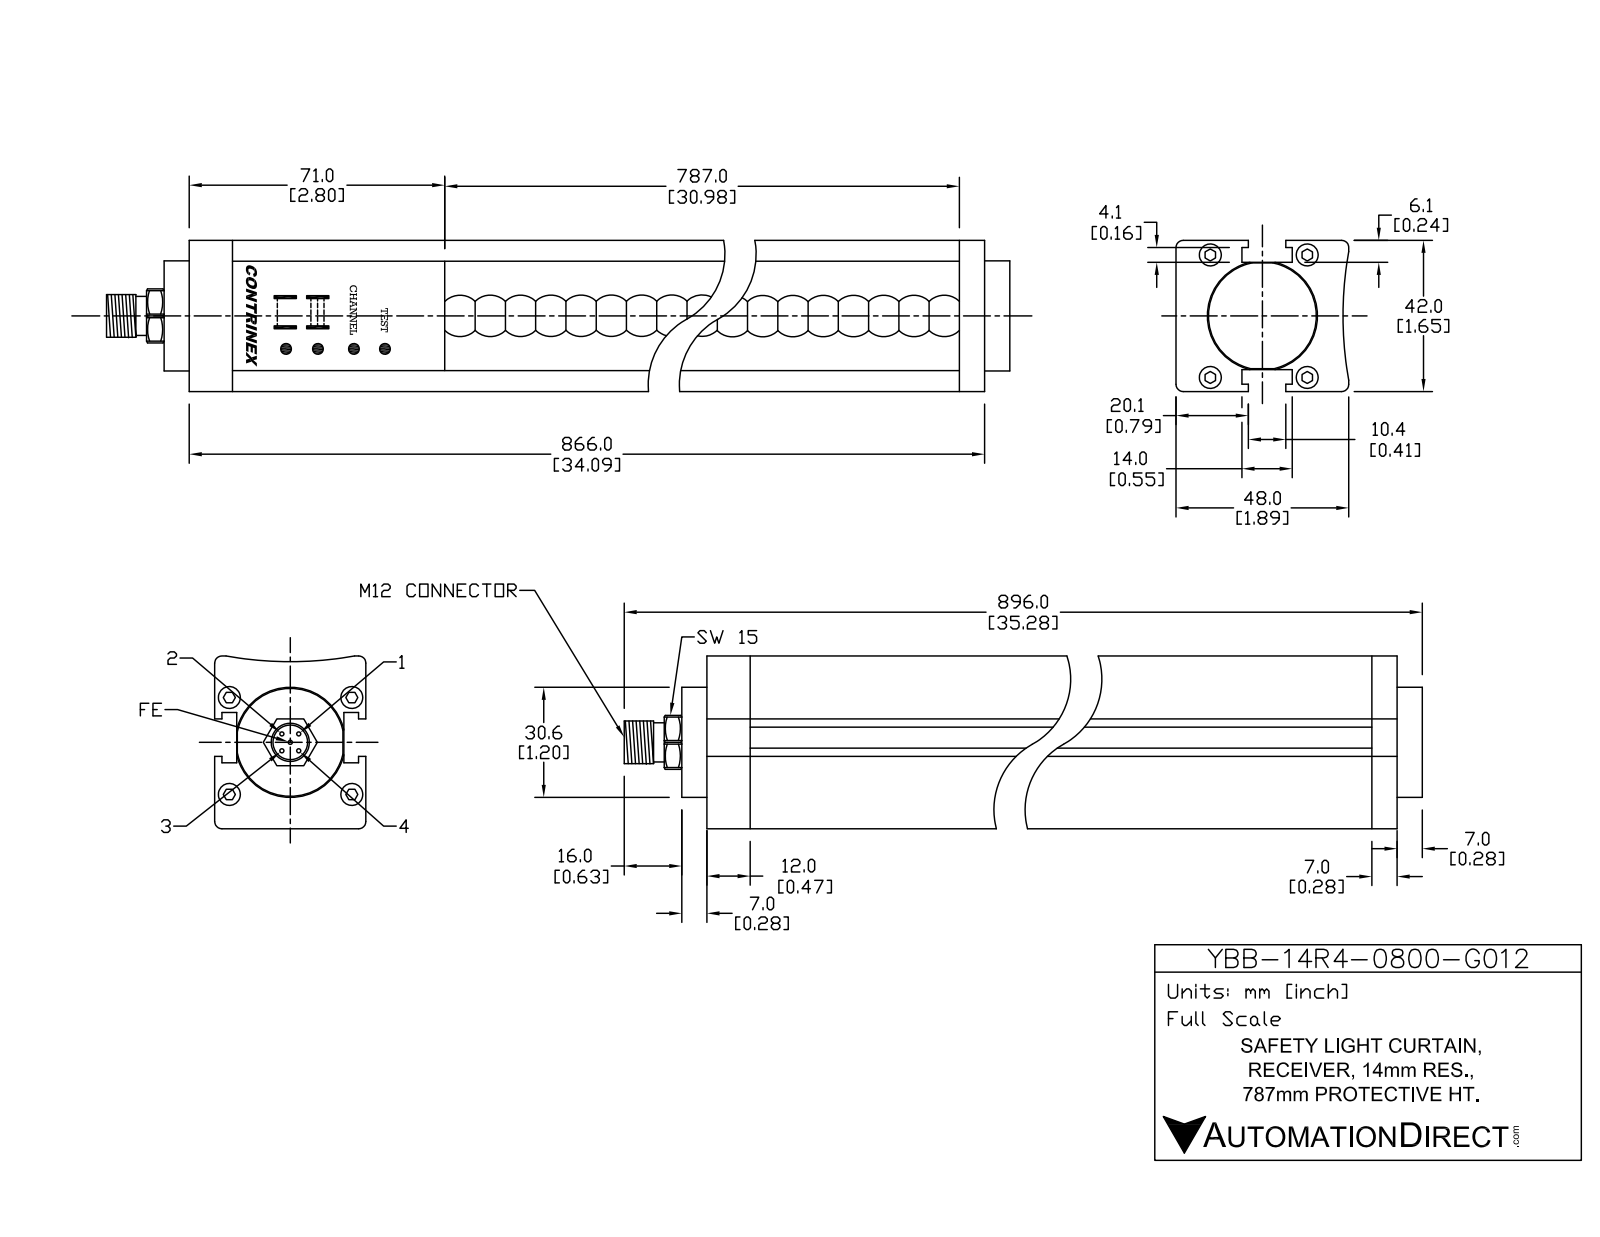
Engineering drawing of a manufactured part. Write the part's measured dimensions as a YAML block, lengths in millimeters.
part_name: "YBB-14R4-0800-G012"
step_written_by: "SolidWorks 2016 (AUTOMOTIVE_DESIGN)"
units: millimeters
bodies: {solids: 19, faces: 440, planar: 208, cylindrical: 168, other: 64}
overall_size: [896, 48, 42]
volume: 1561000
surface_area: 202395
round_holes:
  - {diameter: 6, count: 4}
  - {diameter: 8.5, count: 1}
  - {diameter: 32, count: 1}
round_bosses_or_shafts:
  - {diameter: 1, count: 5}
  - {diameter: 5.5, count: 4}
  - {diameter: 30.6, count: 1}
  - {diameter: 12, count: 1}
  - {diameter: 10.5, count: 1}
partial_cylinders:
  - {radius: 1, count: 48}
  - {radius: 0.5, count: 4}
  - {radius: 0.55, count: 2}
  - {radius: 8.2, count: 1}
  - {radius: 100, count: 1}
face_to_face_distances: [6.3, 35.7, 42, 29.4, 14, 17.2, 31.2, 15.7, 29.7, 46.9]
hole_center_spacings: [21.04, 22.34, 26.9, 34, 43.35]
